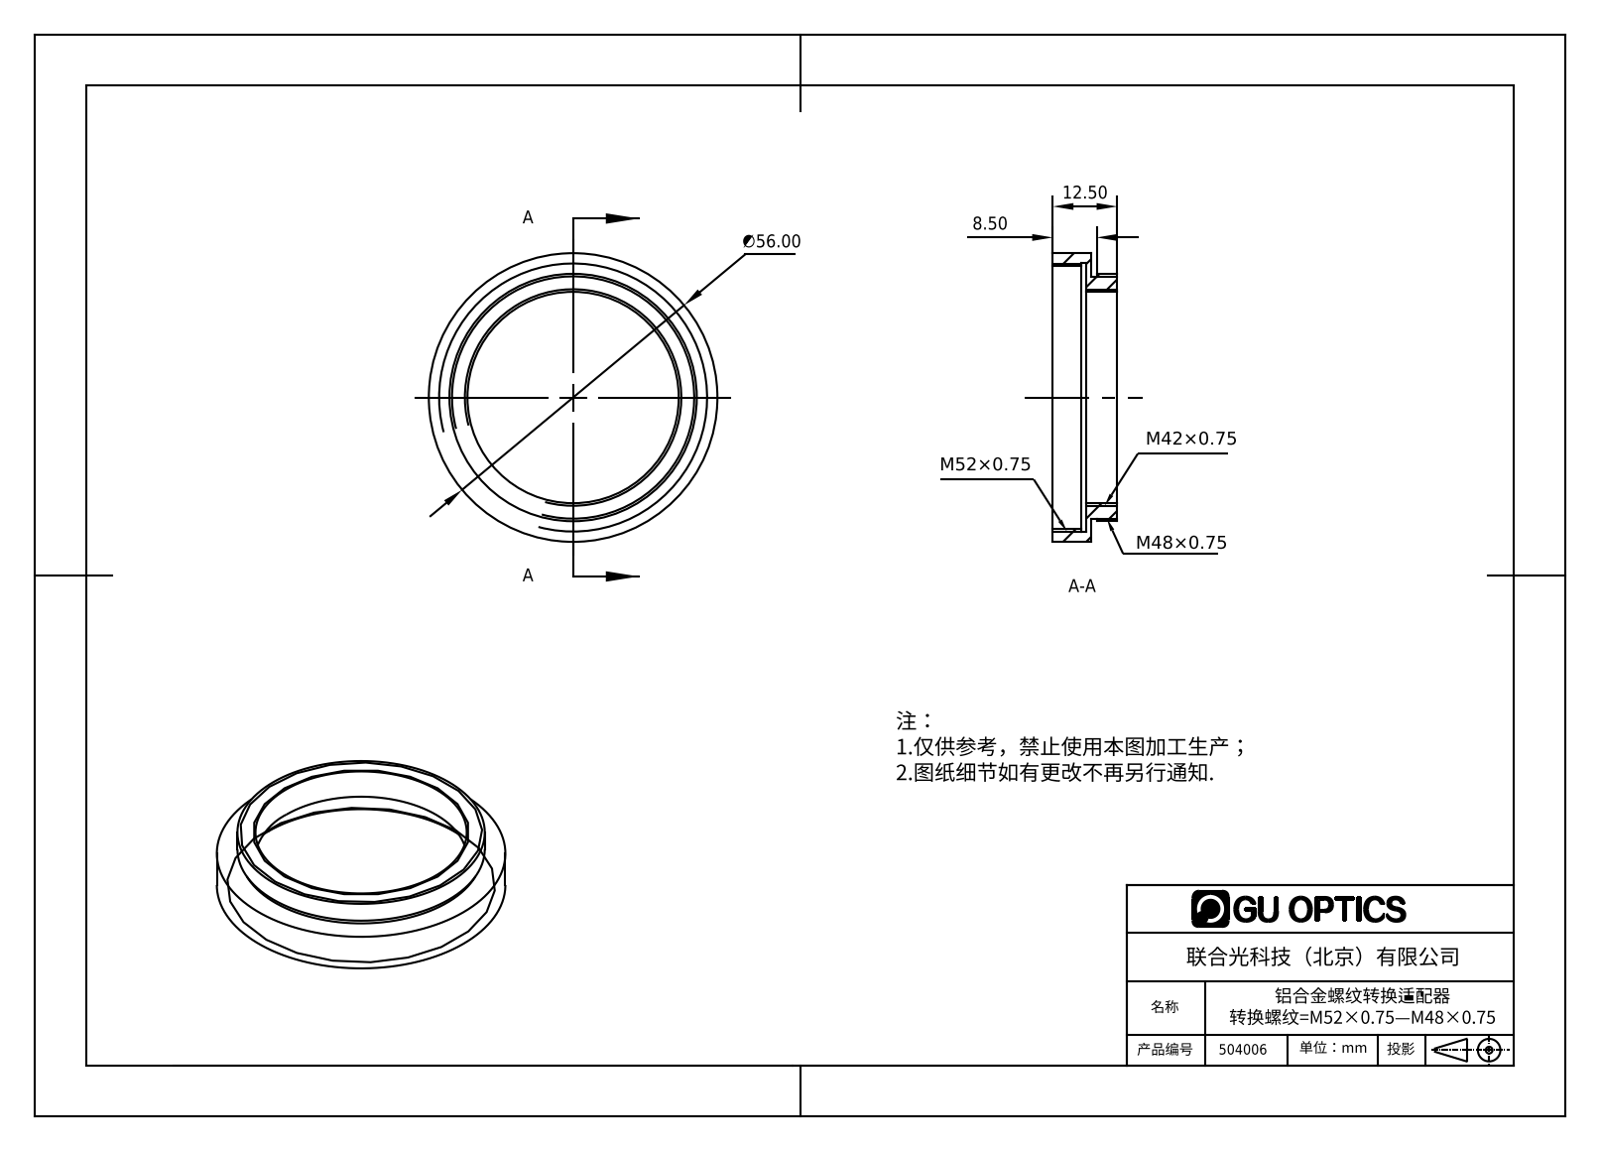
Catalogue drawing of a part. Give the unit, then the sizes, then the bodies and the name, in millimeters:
Units: millimetres
Overall size (bounding box): 56 × 56 × 12.5
Round holes (diameter × count): ⌀41 ×1, ⌀51 ×1, ⌀52.2 ×1
Round bosses / shafts (diameter × count): ⌀56 ×1, ⌀48 ×1, ⌀47 ×1
Main face-to-face distances: 1, 6, 5, 6.5, 7.5, 12.5, 2, 5.5, 7, 8.5
Volume: 6 149 mm³ · Surface area: 6 518 mm²
Bodies: 1 solid, 18 faces (6 planar, 12 cylindrical, 0 other)
Part name (STEP PRODUCT): 504006
STEP written by: SolidWorks 2016 (AUTOMOTIVE_DESIGN)
